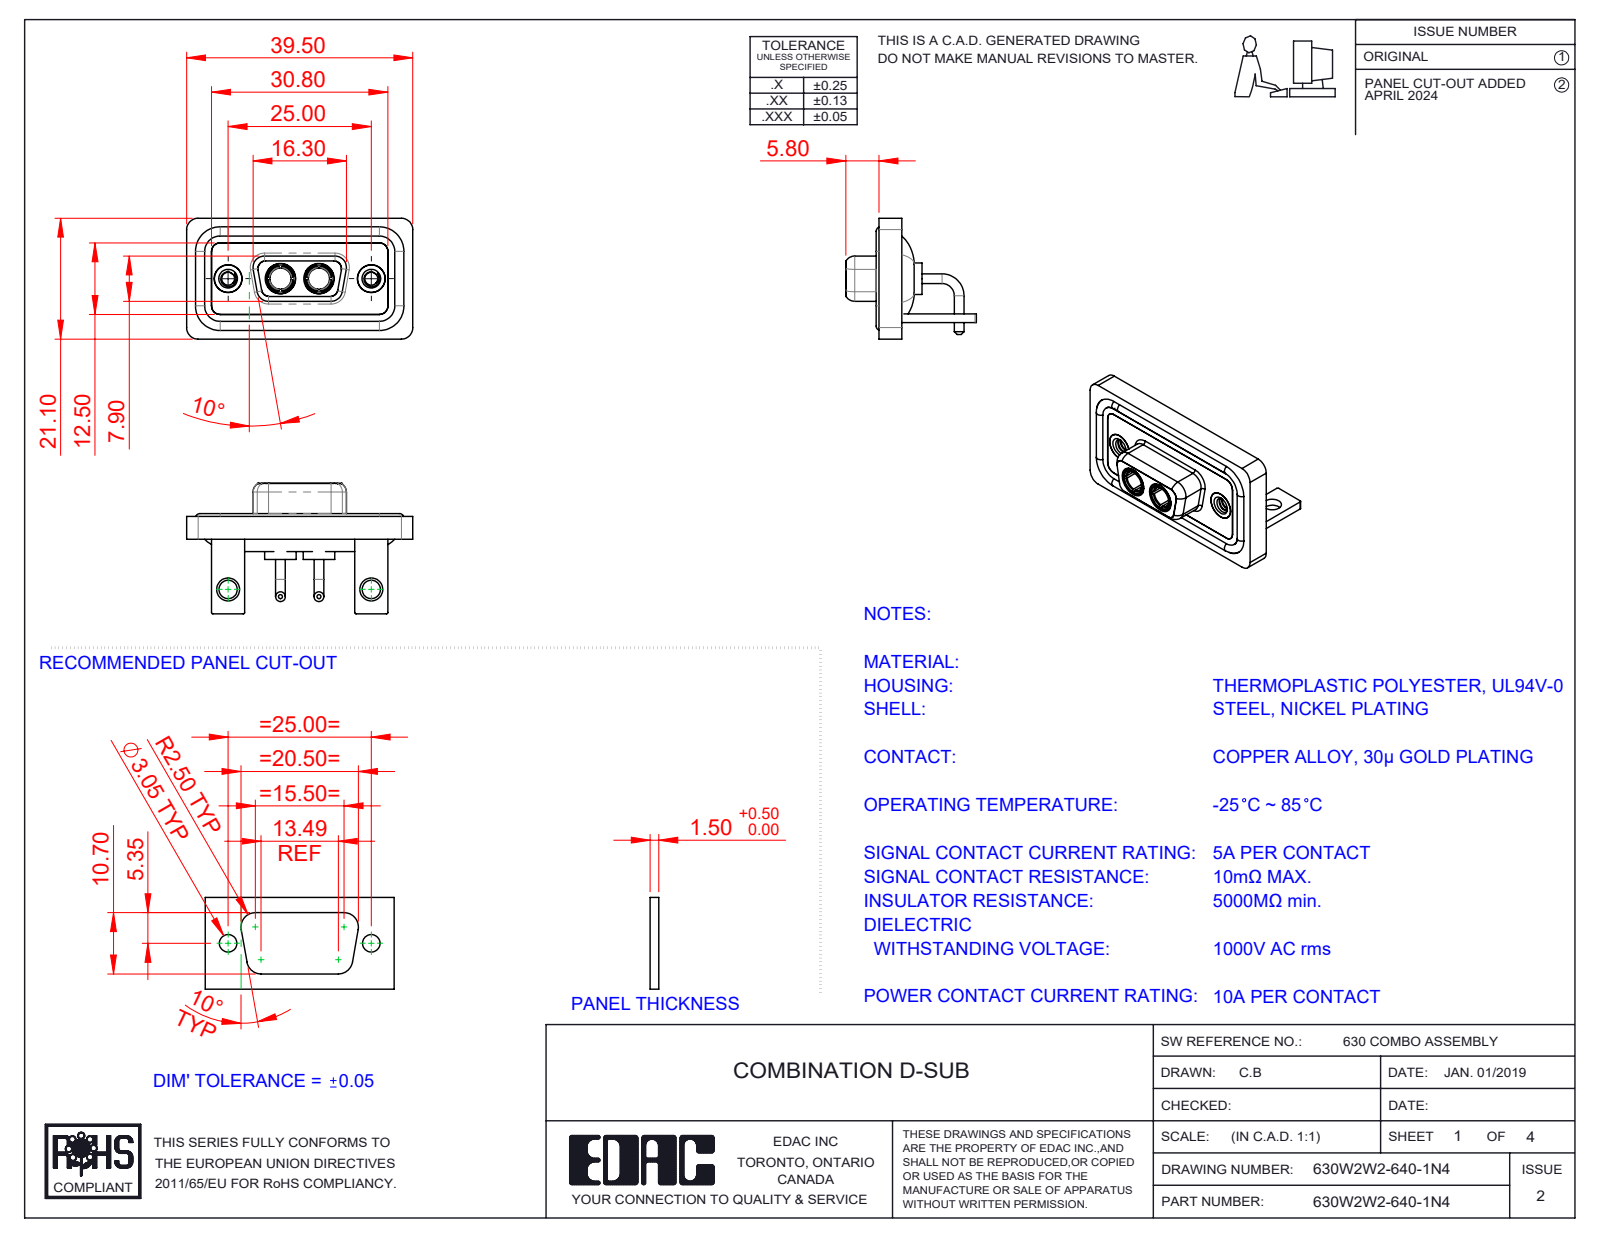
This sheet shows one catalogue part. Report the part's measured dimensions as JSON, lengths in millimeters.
{"part_name": "Power Socket_10A RA; 630Combo Housing_2W2; 630Combo Threaded Rivet_2; 630Combo Shell Front_09 Contacts (+4 more)", "step_written_by": "SolidWorks 2023 (CONFIG_CONTROL_DESIGN)", "units": "millimeters", "bodies": {"solids": 13, "faces": 590, "planar": 183, "cylindrical": 262, "other": 145}, "overall_size": [39.5, 22.8, 21.1], "volume_mm3": 5067, "surface_area_mm2": 8420, "round_holes": [[4.85, 4], [2.26, 2], [3.2, 2], [3.7, 2], [4, 2], [4.05, 2], [5, 2], [5.3, 2]], "round_bosses_or_shafts": [[1.7, 4], [1.6, 4], [5.5, 2], [5.2, 2], [4.96, 2], [4.95, 2], [4.8, 2], [4.75, 2]], "partial_cylinders_radius": [[2, 19], [1.5, 18], [0.25, 16], [1.35, 8], [1.6, 8], [0.5, 5], [0.6, 4], [0.65, 4]], "face_to_face_distances": [0.4, 2.9, 1.5, 1.8, 1.1, 3.7, 0.8, 2.5, 1.6, 3.1], "hole_center_spacings": [9.14, 15.86, 25, 6.72]}
